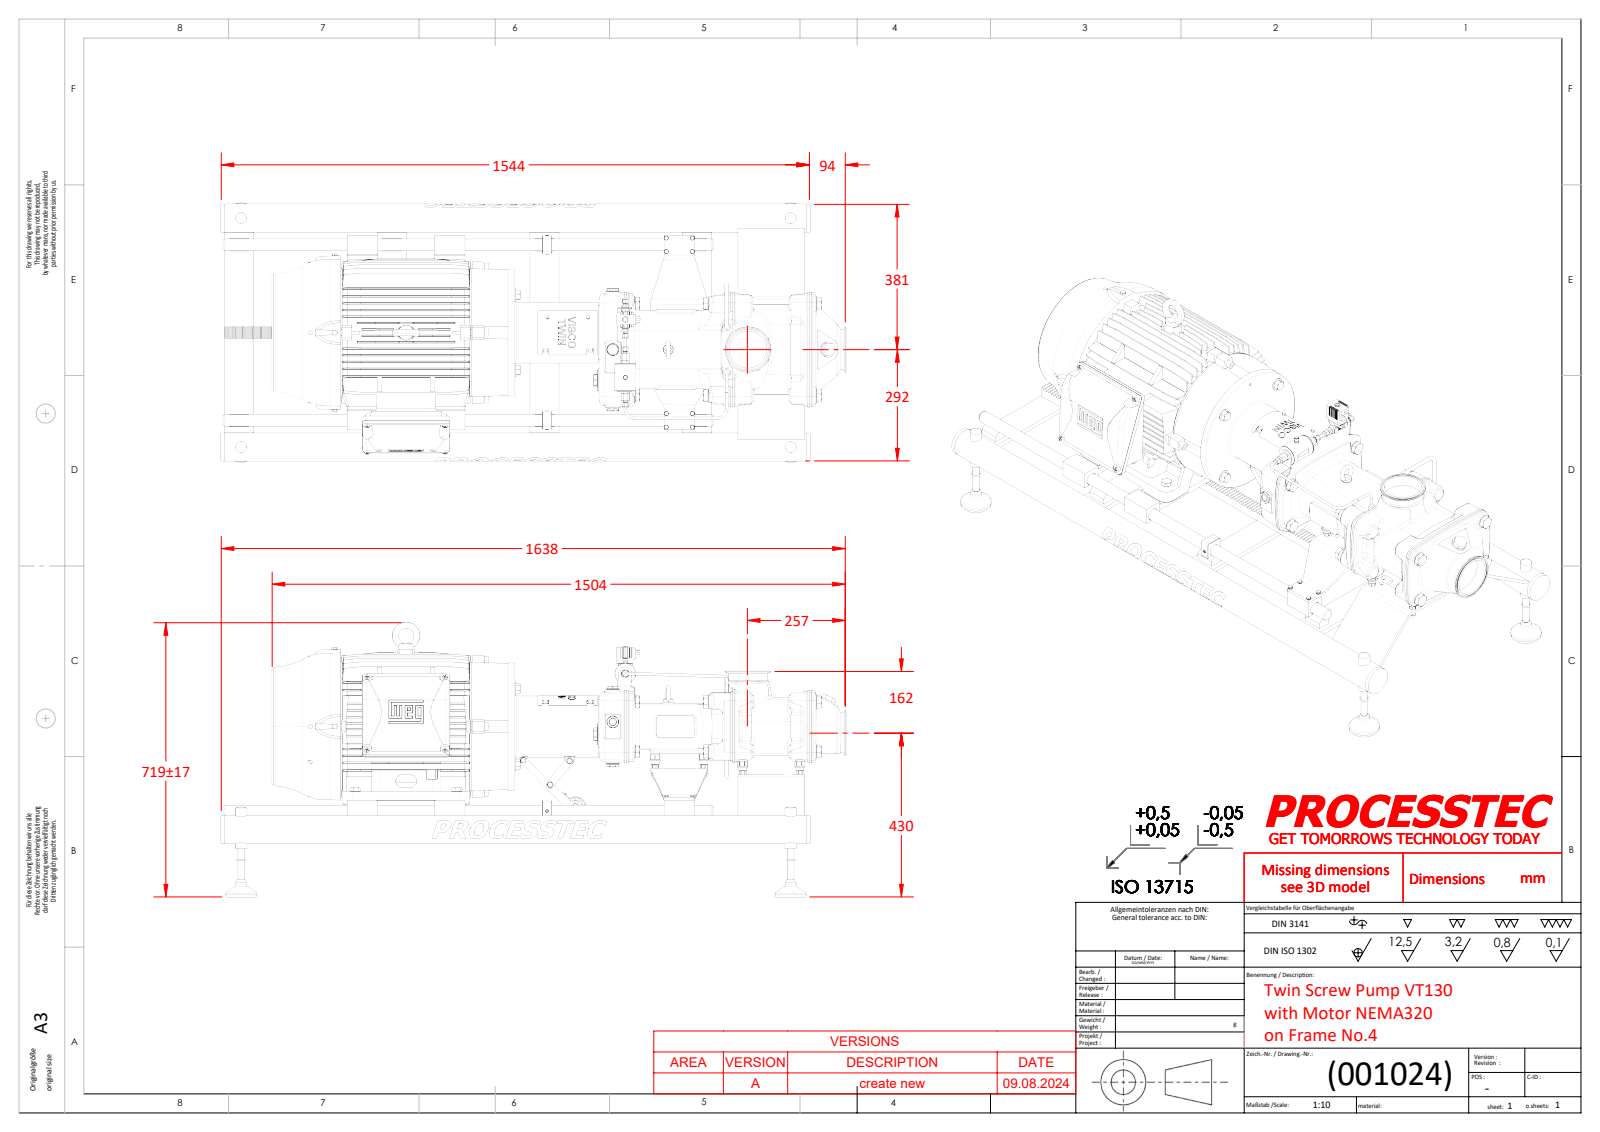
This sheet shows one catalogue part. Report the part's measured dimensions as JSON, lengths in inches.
{"part_name": "Twin Screw Pump VT130 on F4 with NEMA320 - 001024", "step_written_by": "SolidWorks 2023 (AUTOMOTIVE_DESIGN)", "units": "inches", "bodies": {"solids": 0, "faces": 14036, "planar": 4658, "cylindrical": 3713, "other": 5665}, "overall_size": [64.488, 28.325, 26.791], "round_holes": [[0.335, 24], [0.197, 19], [0.551, 14], [0.512, 13], [0.689, 13], [0.268, 12], [0.161, 11], [0.315, 9], [0.413, 9], [0.252, 8], [0.398, 8], [0.404, 8]], "round_bosses_or_shafts": [[0.394, 33], [0.236, 19], [0.945, 17], [0.787, 16], [0.315, 13], [0.728, 12], [0.669, 11], [0.63, 11]], "partial_cylinders_radius": [[0.117, 188], [0.118, 81], [0.059, 54], [0.236, 48], [0.079, 39], [0.354, 30], [0.315, 27], [0.157, 19]], "face_to_face_distances": [13.476, 0.5, 0.315, 29.441, 15.965, 30.886, 17.492, 4.016, 11.949, 48.378], "hole_center_spacings": [18.166, 15.748, 5.091, 9.055, 32.772, 2.165, 24, 31.496]}
